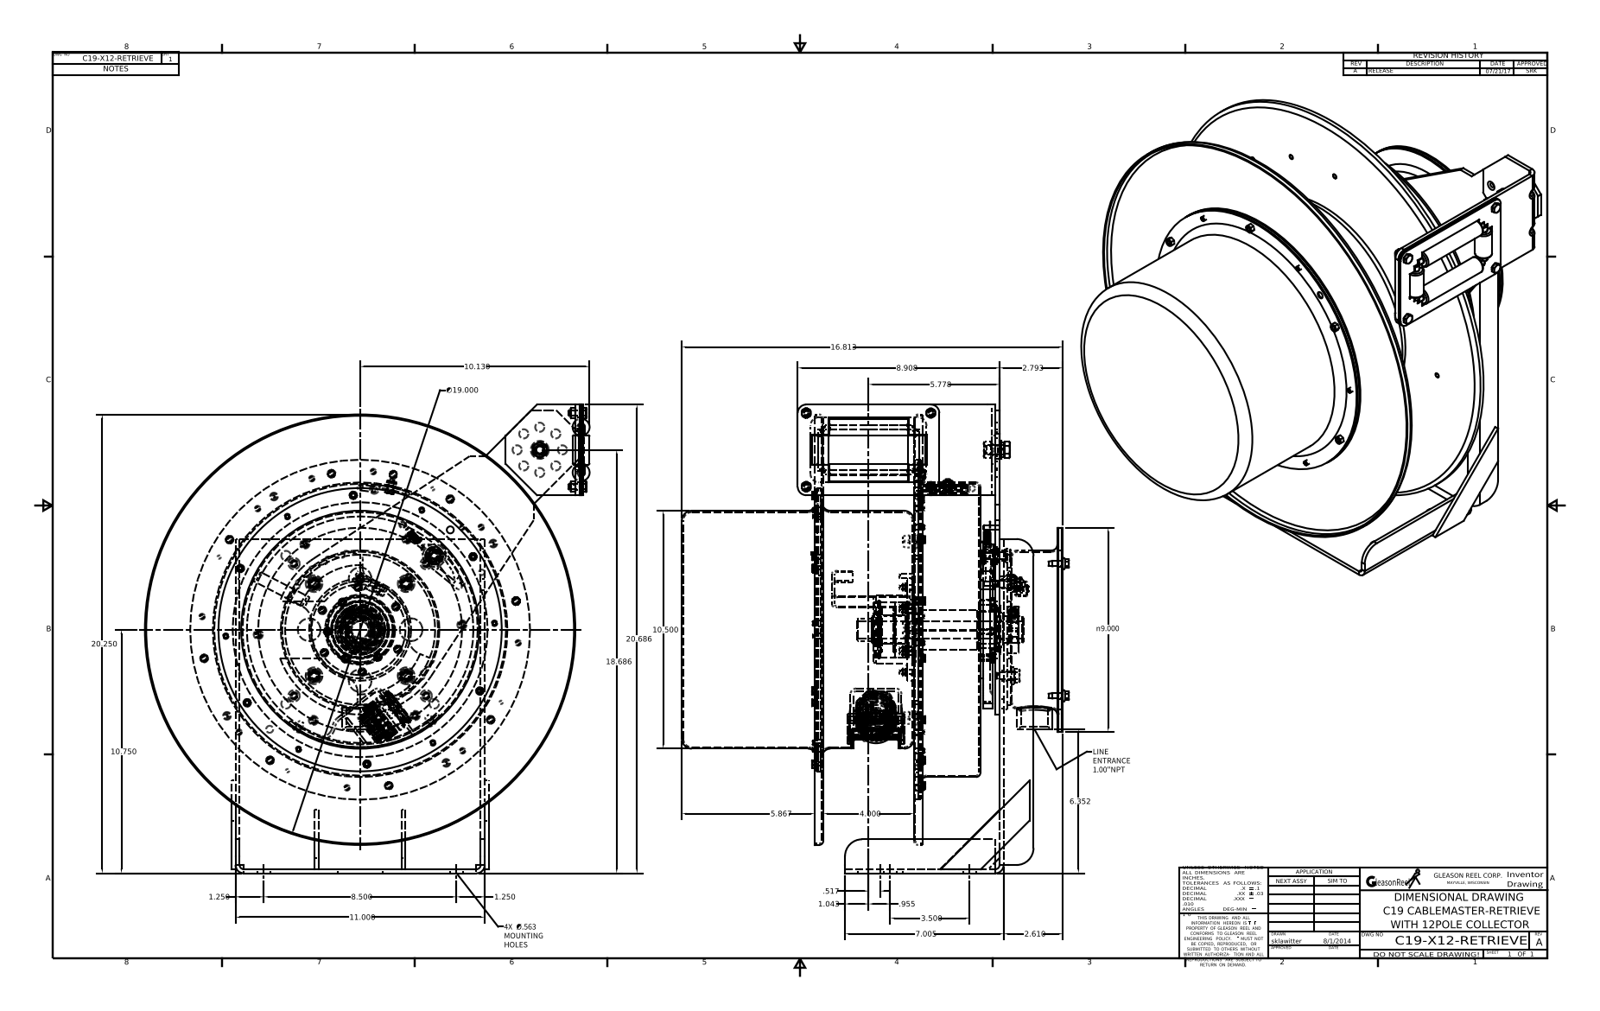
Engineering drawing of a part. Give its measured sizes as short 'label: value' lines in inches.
name: C19-X12-RETRIEVE (SW)
written by: Autodesk Inventor 2016 (AUTOMOTIVE_DESIGN)
unit: in
bodies: 173 solids, 3480 faces (1373 planar, 1017 cylindrical, 1090 other)
size: 20.687 × 19.63 × 17.077
volume: 239.2 in³; area: 5 047 in²
holes: 39× ⌀0.25, 30× ⌀0.197, 26× ⌀0.163, 14× ⌀0.219, 13× ⌀0.406, 12× ⌀0.224, 12× ⌀0.422, 7× ⌀0.156, 7× ⌀0.281, 6× ⌀0.199, 6× ⌀0.211, 6× ⌀1
bosses: 30× ⌀0.197, 10× ⌀0.236, 6× ⌀0.405, 6× ⌀0.394, 6× ⌀0.191, 5× ⌀0.5, 5× ⌀0.457, 5× ⌀0.315
rounds: 67× R0.03, 64× R0.01, 39× R0.015, 18× R0.078, 12× R0.006, 12× R0.06, 8× R0.124, 7× R0.125
face distances: 0.06, 0.185, 0.179, 0.245, 0.125, 4.305, 4.12, 4.06, 2.687, 2.872
hole spacings: 0.765, 1, 1.414, 1.848, 4.063, 5.443, 5.446, 1.25
